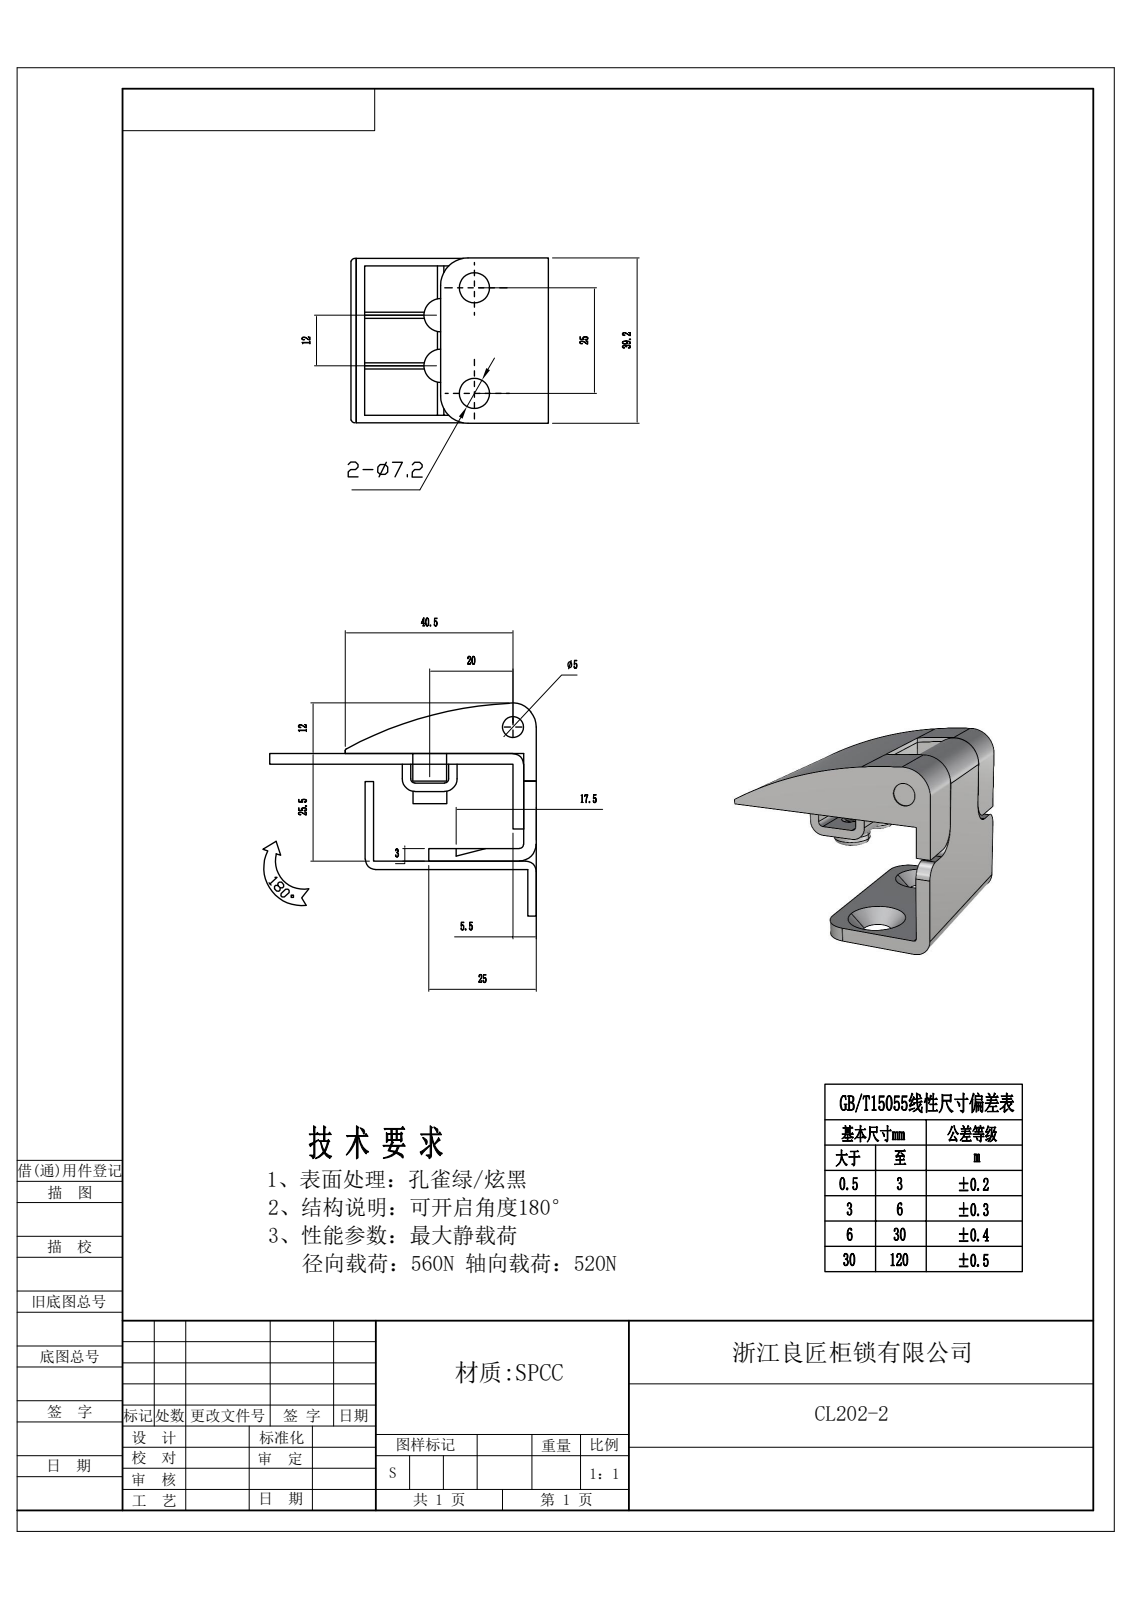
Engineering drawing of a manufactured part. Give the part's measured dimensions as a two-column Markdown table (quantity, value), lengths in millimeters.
| quantity | value |
| --- | --- |
| STEP written by | Rhino 8.5 (CONFIG_CONTROL_DESIGN) |
| units | millimeters |
| bodies | 7 solids, 480 faces (234 planar, 202 cylindrical, 44 other) |
| overall size | 231.73 × 40 × 25.05 |
| volume | 15 409 mm³ |
| surface area | 30 450 mm² |
| round holes (diameter × count) | 8 × 4, 5 × 2 |
| round bosses / shafts (diameter × count) | 4.5 × 4, 11 × 2, 5 × 2, 4.6 × 2, 3.23 × 2 |
| partial cylindrical surfaces (radius × count) | 1 × 8, 3 × 6, 5 × 6, 0.5 × 2, 3.5 × 2, 4 × 2, 4.55 × 2, 89.02 × 2 |
| main face-to-face distances | 3, 157.98, 1.8, 37.55, 10.91, 28.44, 9.11, 26.64, 39.35, 41.26 |
| hole center spacings | 157.98, 12.35, 158.46 |
